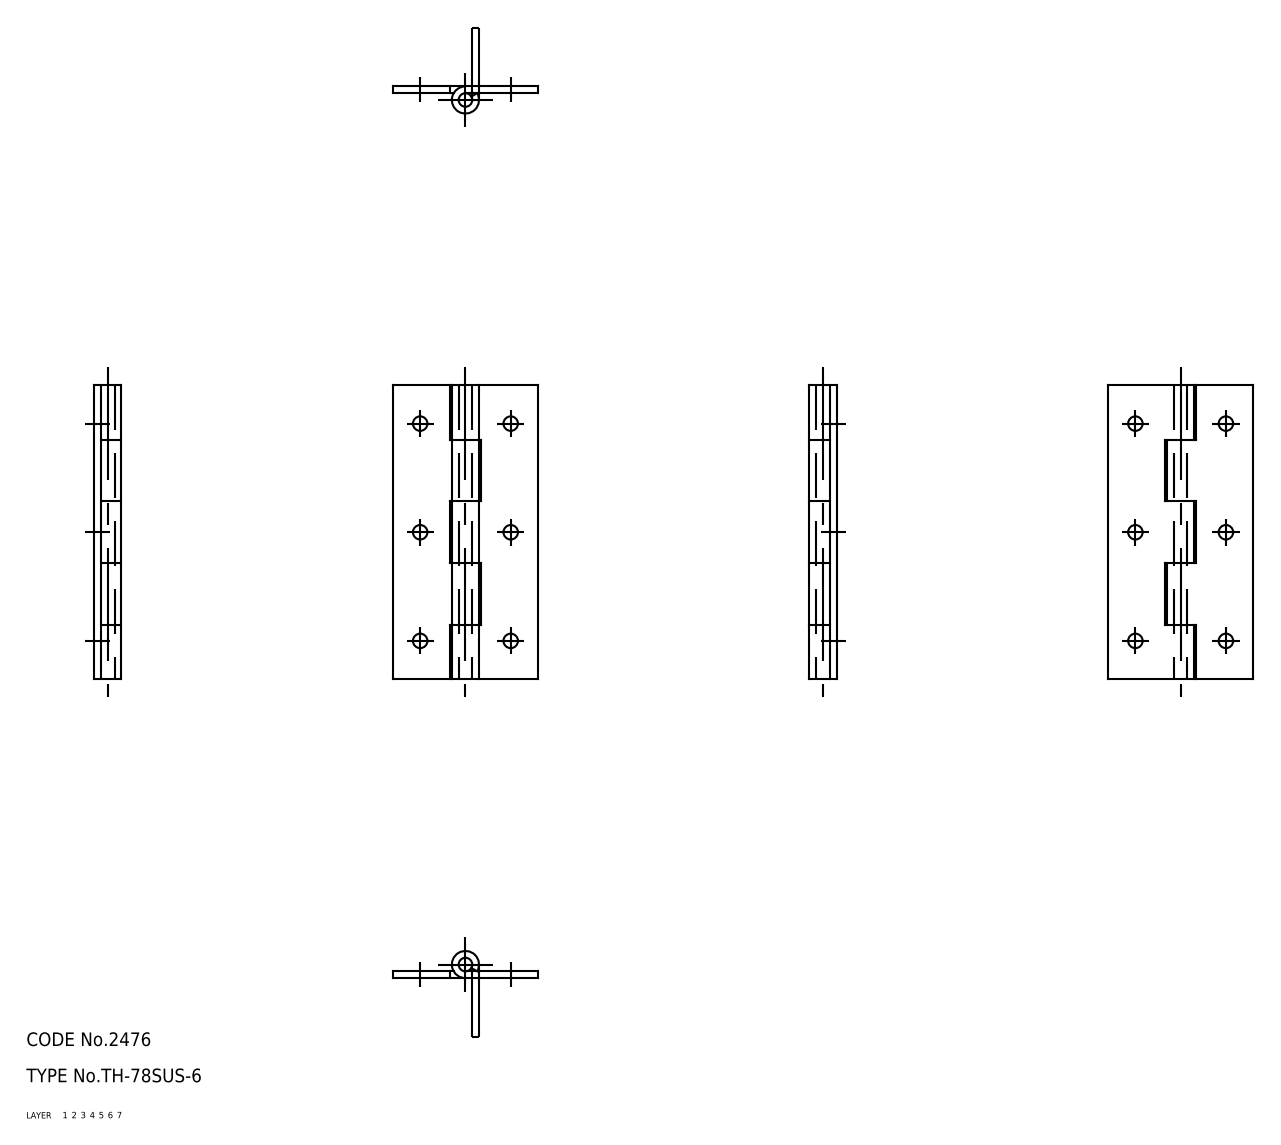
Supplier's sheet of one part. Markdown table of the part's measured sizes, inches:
| quantity | value |
| --- | --- |
| part name | hinge piece_B; hinge piece_A; shaft; TH_78SUS_6_17353_36 |
| STEP written by | CADfix (AUTOMOTIVE_DESIGN) |
| units | inches |
| bodies | 3 solids, 54 faces (0 planar, 0 cylindrical, 54 other) |
| overall size | 2.559 × 1.26 × 0.236 |
| volume | 0.263 in³ |
| surface area | 10.15 in² |
